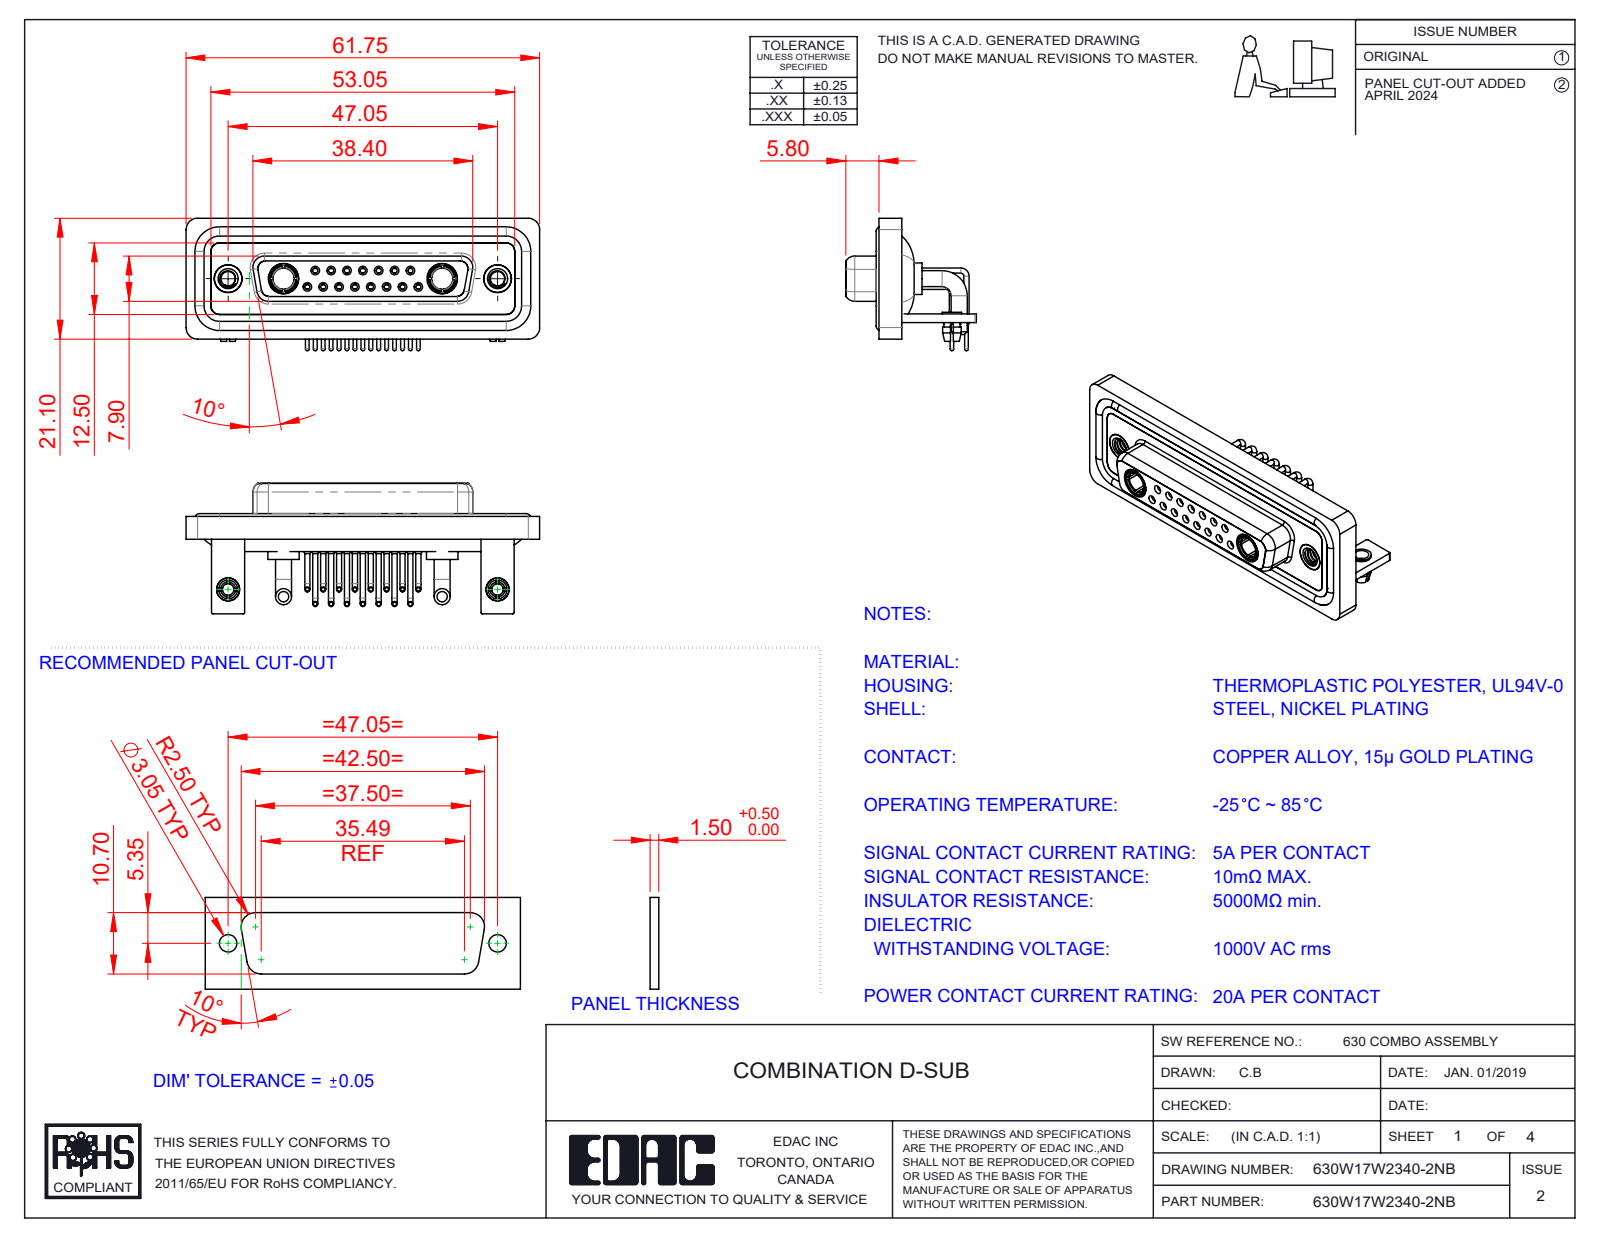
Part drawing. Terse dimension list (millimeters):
name: 630Combo Shell Front_25 Contacts; 630Combo Shell Rear_25 Contacts; 630Combo Contact Row 1_50 Contacts; Power Socket_20A RA (+7 more)
written by: SolidWorks 2023 (CONFIG_CONTROL_DESIGN)
unit: mm
bodies: 30 solids, 1471 faces (456 planar, 637 cylindrical, 378 other)
size: 61.75 × 23.12 × 22.8
volume: 8 882 mm³; area: 15 479 mm²
holes: 17× ⌀2, 15× ⌀0.9, 15× ⌀1.1, 15× ⌀1.5, 8× ⌀1.6, 7× ⌀1.7, 4× ⌀2.5, 4× ⌀4.85, 2× ⌀3.2, 2× ⌀3.7, 2× ⌀4, 2× ⌀4.05
bosses: 15× ⌀0.9, 15× ⌀0.65, 11× ⌀1.6, 4× ⌀2.8, 2× ⌀5.5, 2× ⌀5.2, 2× ⌀4.96, 2× ⌀4.95
rounds: 19× R2, 18× R1.5, 16× R0.25, 8× R1.35, 8× R1.6, 5× R0.5, 4× R0.6, 4× R0.65
face distances: 0.4, 1.8, 2.9, 3.7, 1.5, 4.1, 1.1, 1.4, 1.6, 3.1
hole spacings: 3.16, 2.77, 5.54, 8.31, 5.04, 7.49, 11.08, 5.03
